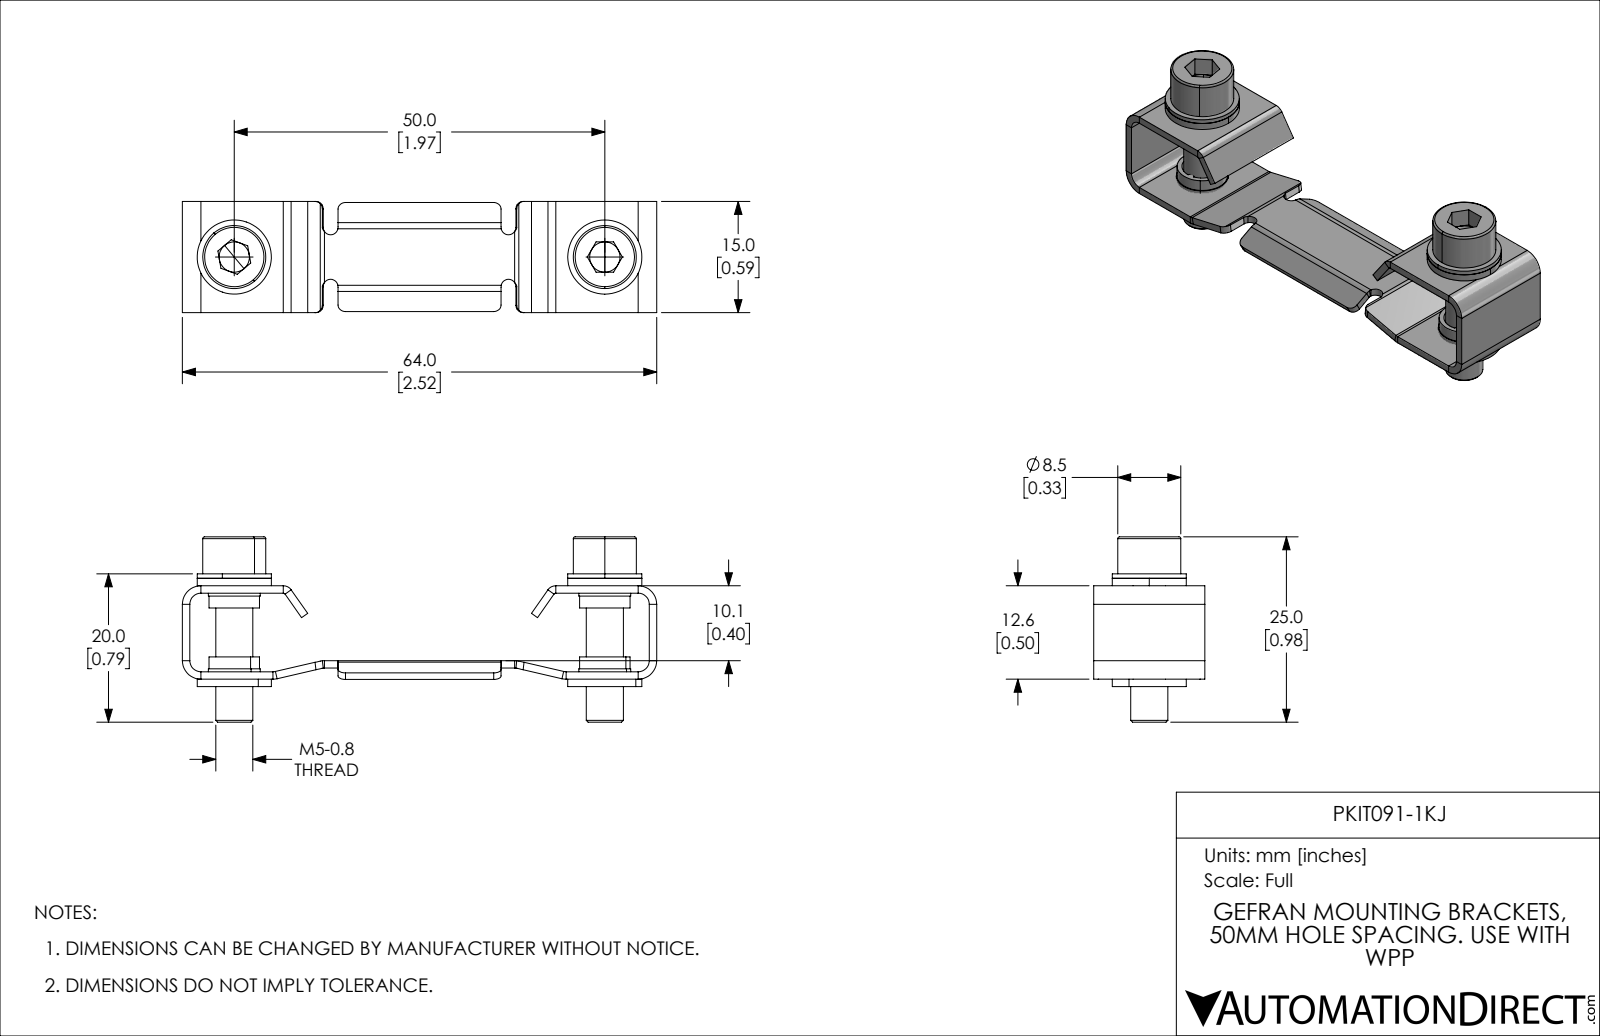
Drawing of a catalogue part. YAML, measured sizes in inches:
part_name: "PKIT091-1KJ"
step_written_by: "SolidWorks 2021 (CONFIG_CONTROL_DESIGN)"
units: inches
bodies: {solids: 9, faces: 334, planar: 172, cylindrical: 142, other: 20}
overall_size: [2.52, 0.984, 0.591]
volume: 0.202
surface_area: 9.52
round_holes:
  - {diameter: 0.217, count: 2}
  - {diameter: 0.272, count: 2}
round_bosses_or_shafts:
  - {diameter: 0.394, count: 2}
  - {diameter: 0.335, count: 2}
  - {diameter: 0.276, count: 2}
  - {diameter: 0.268, count: 2}
  - {diameter: 0.197, count: 2}
partial_cylinders:
  - {radius: 0.018, count: 16}
  - {radius: 0.02, count: 12}
  - {radius: 0.039, count: 12}
  - {radius: 0.059, count: 8}
  - {radius: 0.098, count: 8}
  - {radius: 0.012, count: 2}
  - {radius: 0.029, count: 2}
  - {radius: 0.051, count: 2}
face_to_face_distances: [0.039, 0.496, 0.457, 0.059, 0.398, 0.437, 0.079, 0.535, 0.098, 0.417]
hole_center_spacings: [1.969]
